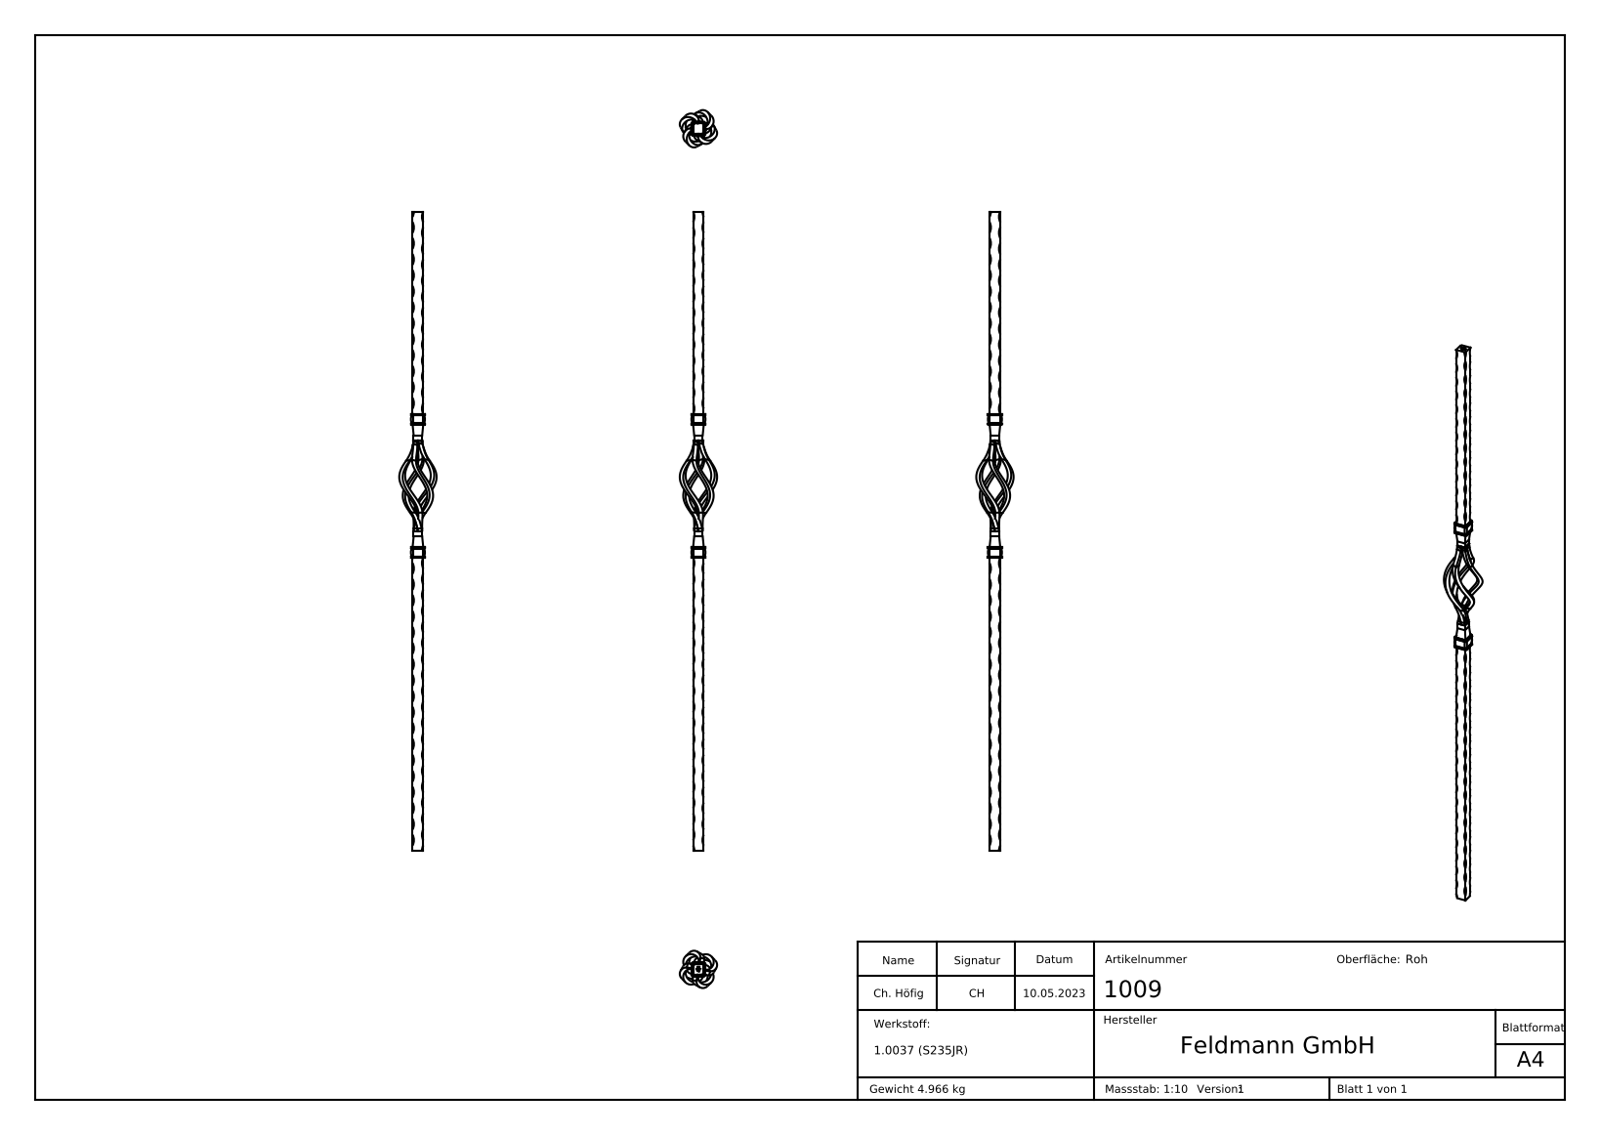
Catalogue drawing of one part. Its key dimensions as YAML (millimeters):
part_name: "1009"
step_written_by: "SolidWorks 2018 (CONFIG_CONTROL_DESIGN)"
units: millimeters
bodies: {solids: 4, faces: 767, planar: 255, cylindrical: 128, other: 384}
overall_size: [1200, 70.03, 70.03]
volume: 636705
surface_area: 130825
round_bosses_or_shafts:
  - {diameter: 16, count: 1}
partial_cylinders:
  - {radius: 0.5, count: 68}
  - {radius: 19, count: 8}
  - {radius: 3.5, count: 4}
face_to_face_distances: [20, 20.2, 2.98, 2, 18, 20.4, 2.2, 18.2, 16, 250]
